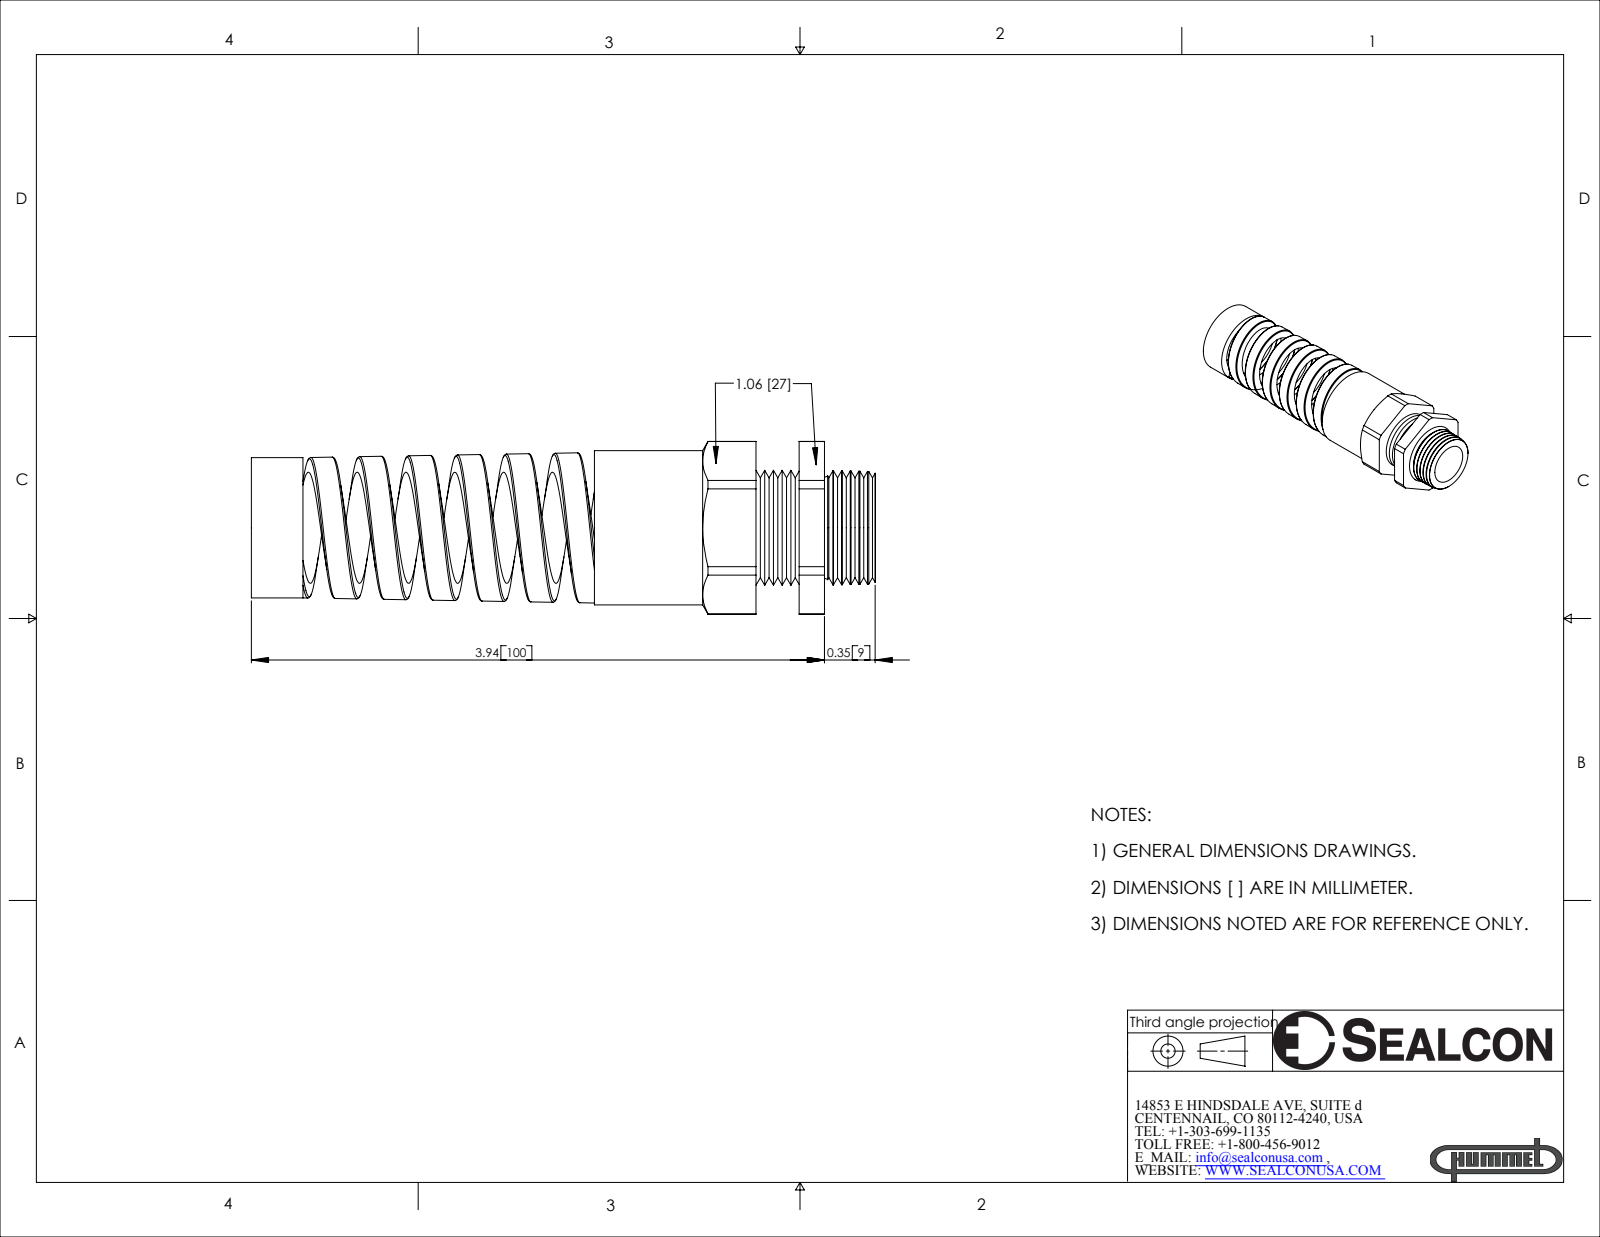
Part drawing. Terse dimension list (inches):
name: CF22MR
written by: SolidWorks 2007 (CONFIG_CONTROL_DESIGN)
unit: in
bodies: 1 solid, 139 faces (19 planar, 34 cylindrical, 86 other)
size: 4.29 × 1.187 × 1.06
volume: 1.533 in³; area: 24.6 in²
holes: 1× ⌀0.47, 1× ⌀0.764, 1× ⌀0.79
bosses: 1× ⌀1.06, 1× ⌀0.964
rounds: 1× R0.594
face distances: 1.06, 1.407, 1.111, 0.297, 1.581, 0.471, 0.174, 2.359, 3.469, 3.766
